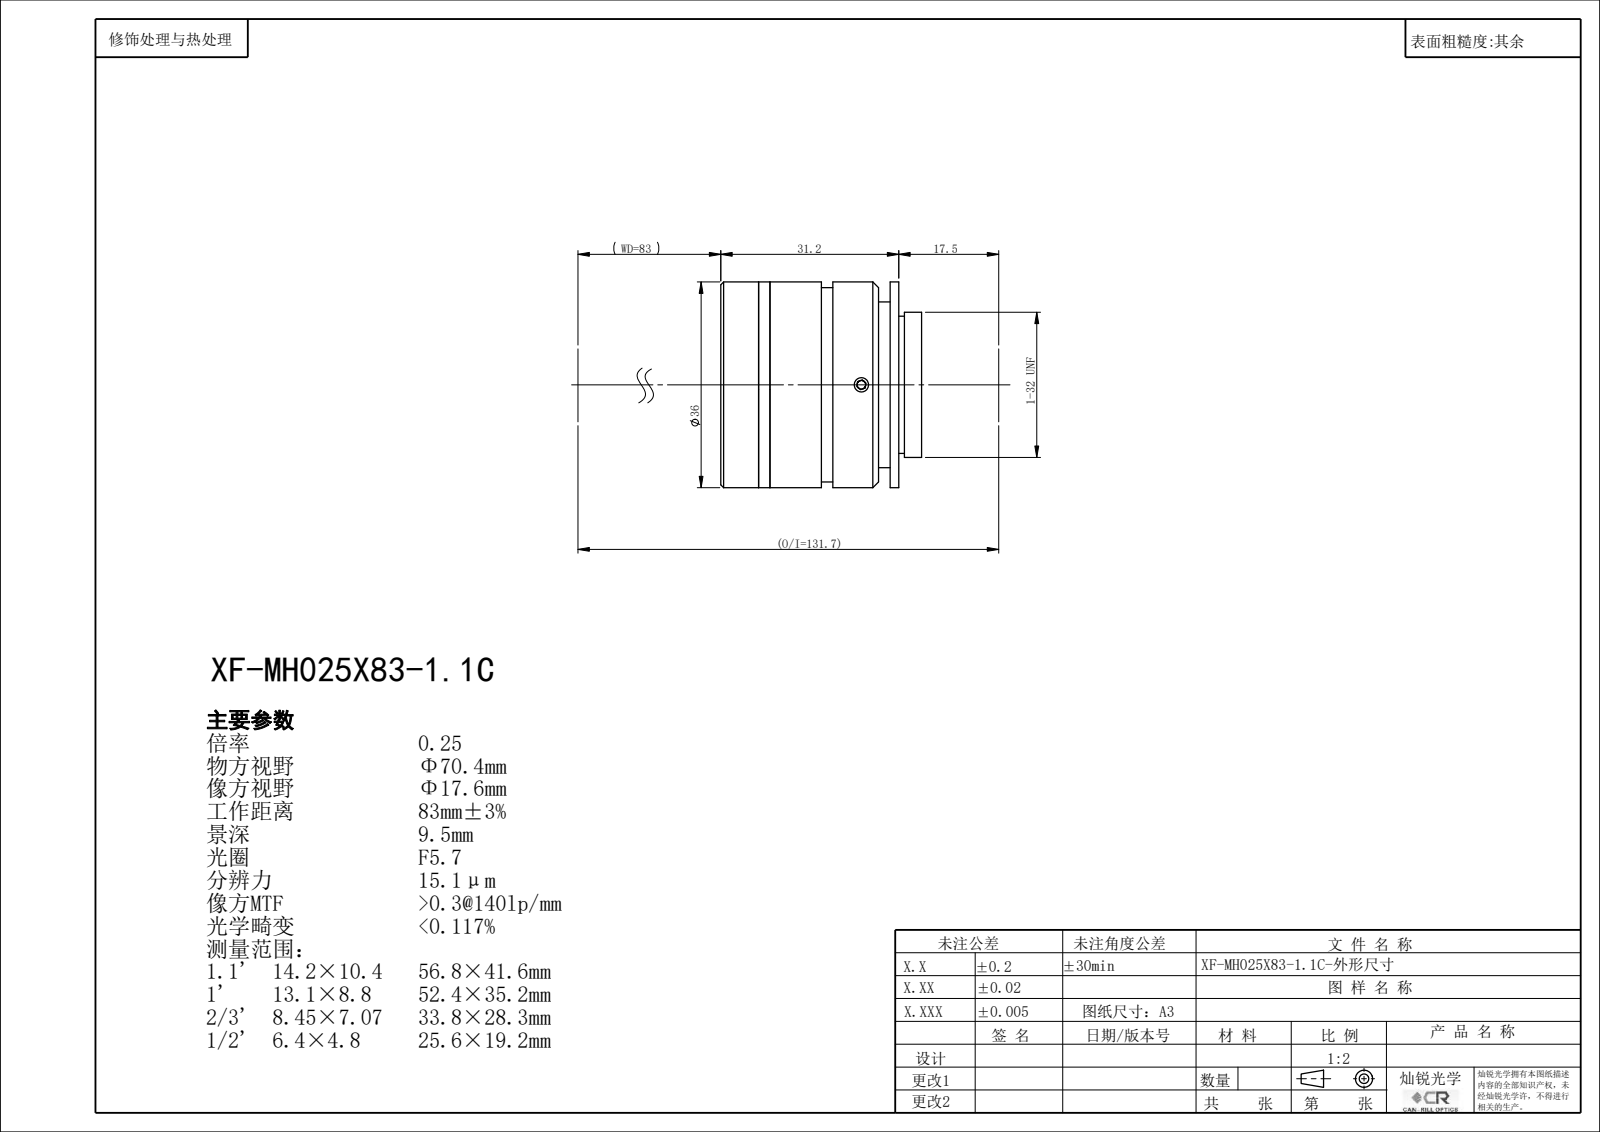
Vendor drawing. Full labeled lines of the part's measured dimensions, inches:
Part name (STEP PRODUCT): XF-MH025X83-1.1C
STEP written by: SolidWorks 2022 (CONFIG_CONTROL_DESIGN)
Units: inches
Bodies: 0 solids, 101 faces (44 planar, 36 cylindrical, 21 other)
Overall size (bounding box): 1.417 × 1.417 × 1.384
Round holes (diameter × count): ⌀0.098 ×3, ⌀0.394 ×1, ⌀0.591 ×1, ⌀0.685 ×1, ⌀0.846 ×1, ⌀0.98 ×1, ⌀1.024 ×1
Round bosses / shafts (diameter × count): ⌀1.417 ×1, ⌀1.339 ×1, ⌀1.142 ×1, ⌀1 ×1, ⌀0.945 ×1
Main face-to-face distances: 0.079, 0.966, 0.887, 0.261, 0.339, 1.227, 0.059, 1.168, 0.907, 0.828
